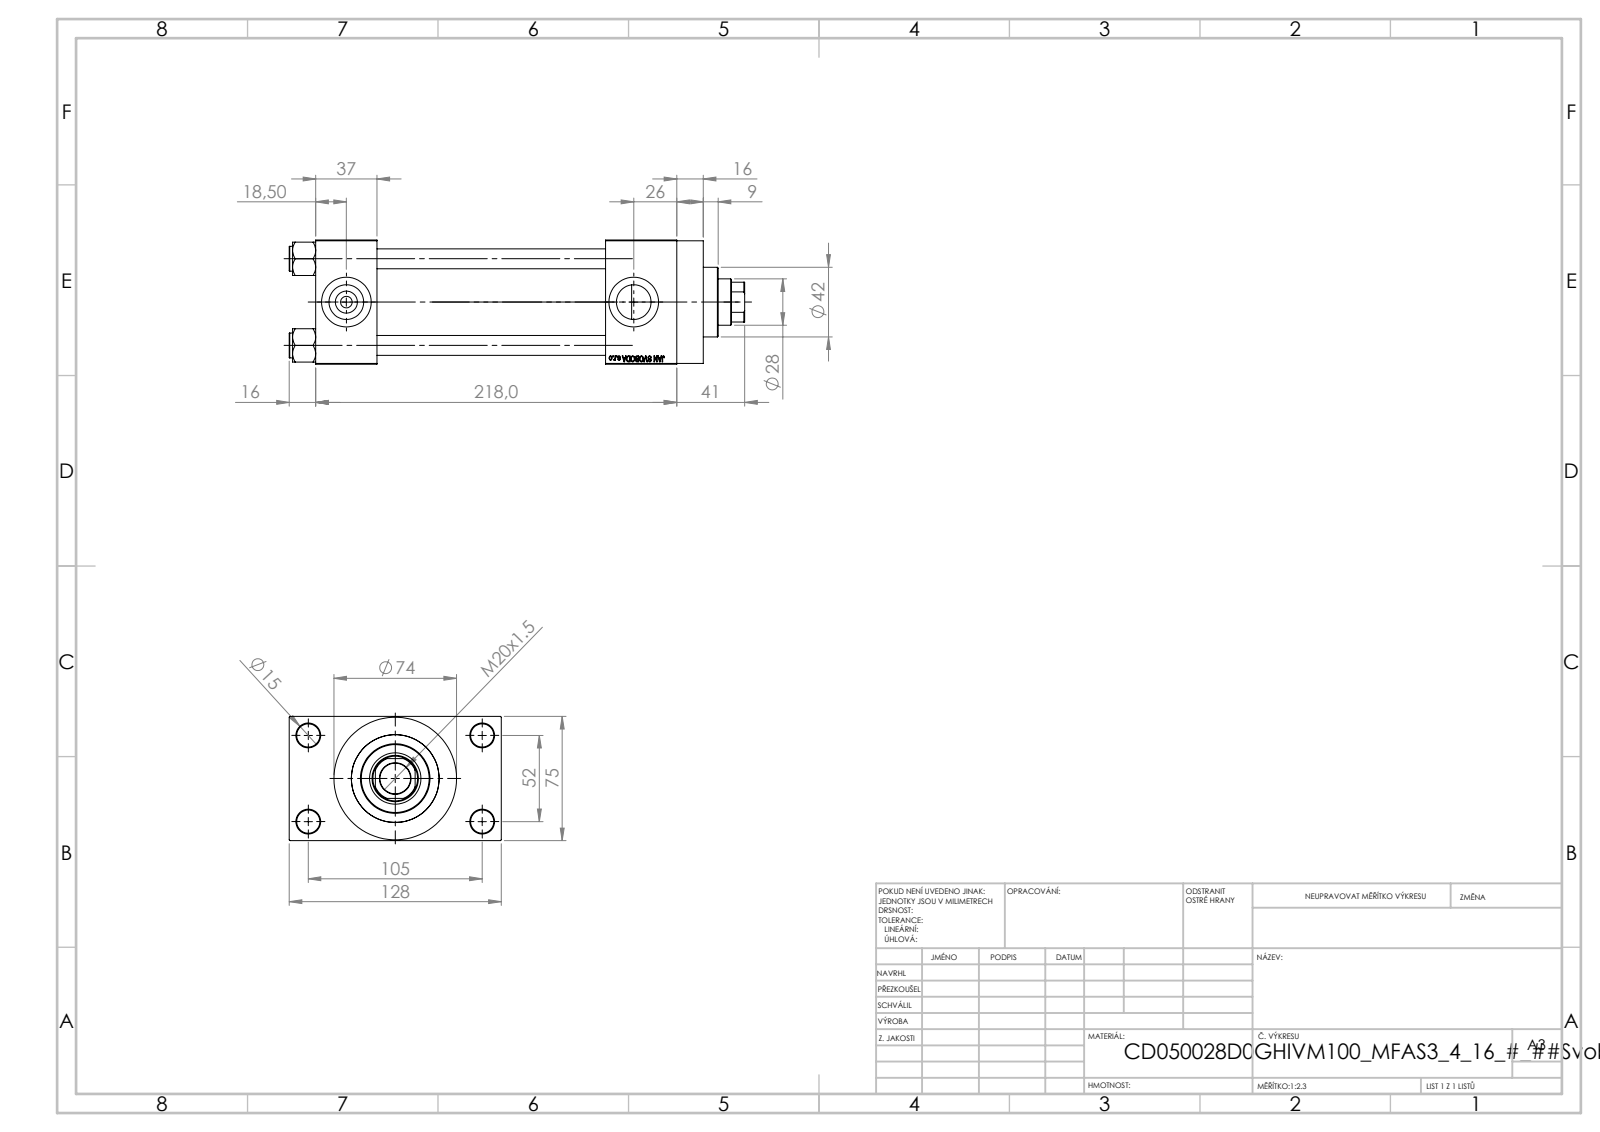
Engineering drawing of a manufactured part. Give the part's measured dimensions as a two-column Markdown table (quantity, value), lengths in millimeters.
| quantity | value |
| --- | --- |
| part name | V215CD_NUT_M5_D; V215CD_D_TYCINKA; V215CD_D_Body; V215CD_VC_A (+1 more) |
| STEP written by | SolidWorks 2019 (CONFIG_CONTROL_DESIGN) |
| units | millimeters |
| bodies | 11 solids, 1103 faces (497 planar, 88 cylindrical, 518 other) |
| overall size | 275 × 128 × 75 |
| volume | 931 622 mm³ |
| surface area | 216 350 mm² |
| round holes (diameter × count) | 12 × 4, 14 × 4, 7 × 2, 20.96 × 2, 30 × 2, 18.5 × 1, 28 × 1, 31 × 1, 41 × 1, 50 × 1, 53 × 1 |
| round bosses / shafts (diameter × count) | 15 × 4, 74 × 1, 56 × 1, 42 × 1 |
| partial cylindrical surfaces (radius × count) | 13.5 × 1 |
| main face-to-face distances | 75, 138, 37, 175, 26.5, 218, 181, 43, 101.5, 16 |
| hole center spacings | 26.35, 36.98, 52.3, 58.43, 58.59, 78.65, 94.37, 52 |
